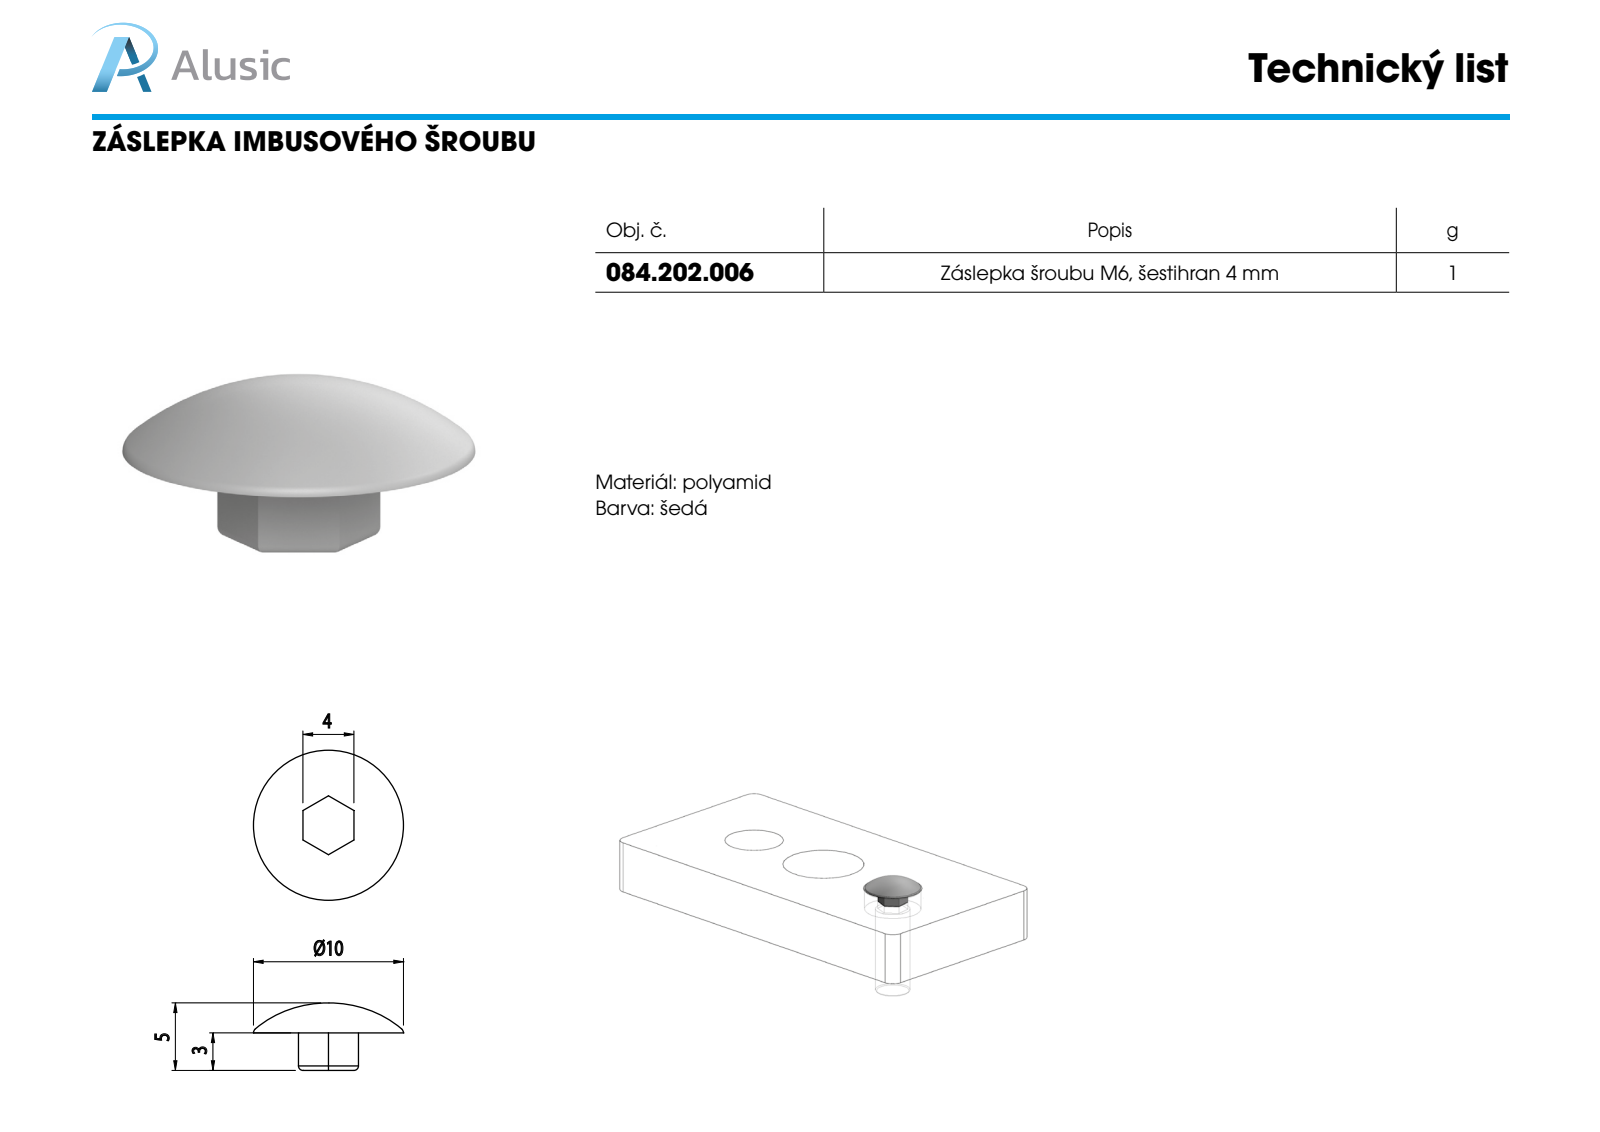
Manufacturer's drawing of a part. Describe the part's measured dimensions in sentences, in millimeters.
The part is named "084.202.006". Its 3-D file was written by "SolidWorks 2011 (CONFIG_CONTROL_DESIGN)". It is 1 solid with 37 faces: 15 planar, 18 cylindrical and 4 other. Overall it measures 10 by 10 by 4.5 millimeters. Its volume is 114 cubic millimeters and its surface area 220 square millimeters. Partial cylindrical surfaces (rounded edges, fillets, slot ends): 18 of radius 0.3. The main face-to-face distances are 4, 3, 1, 2, 2.5.
